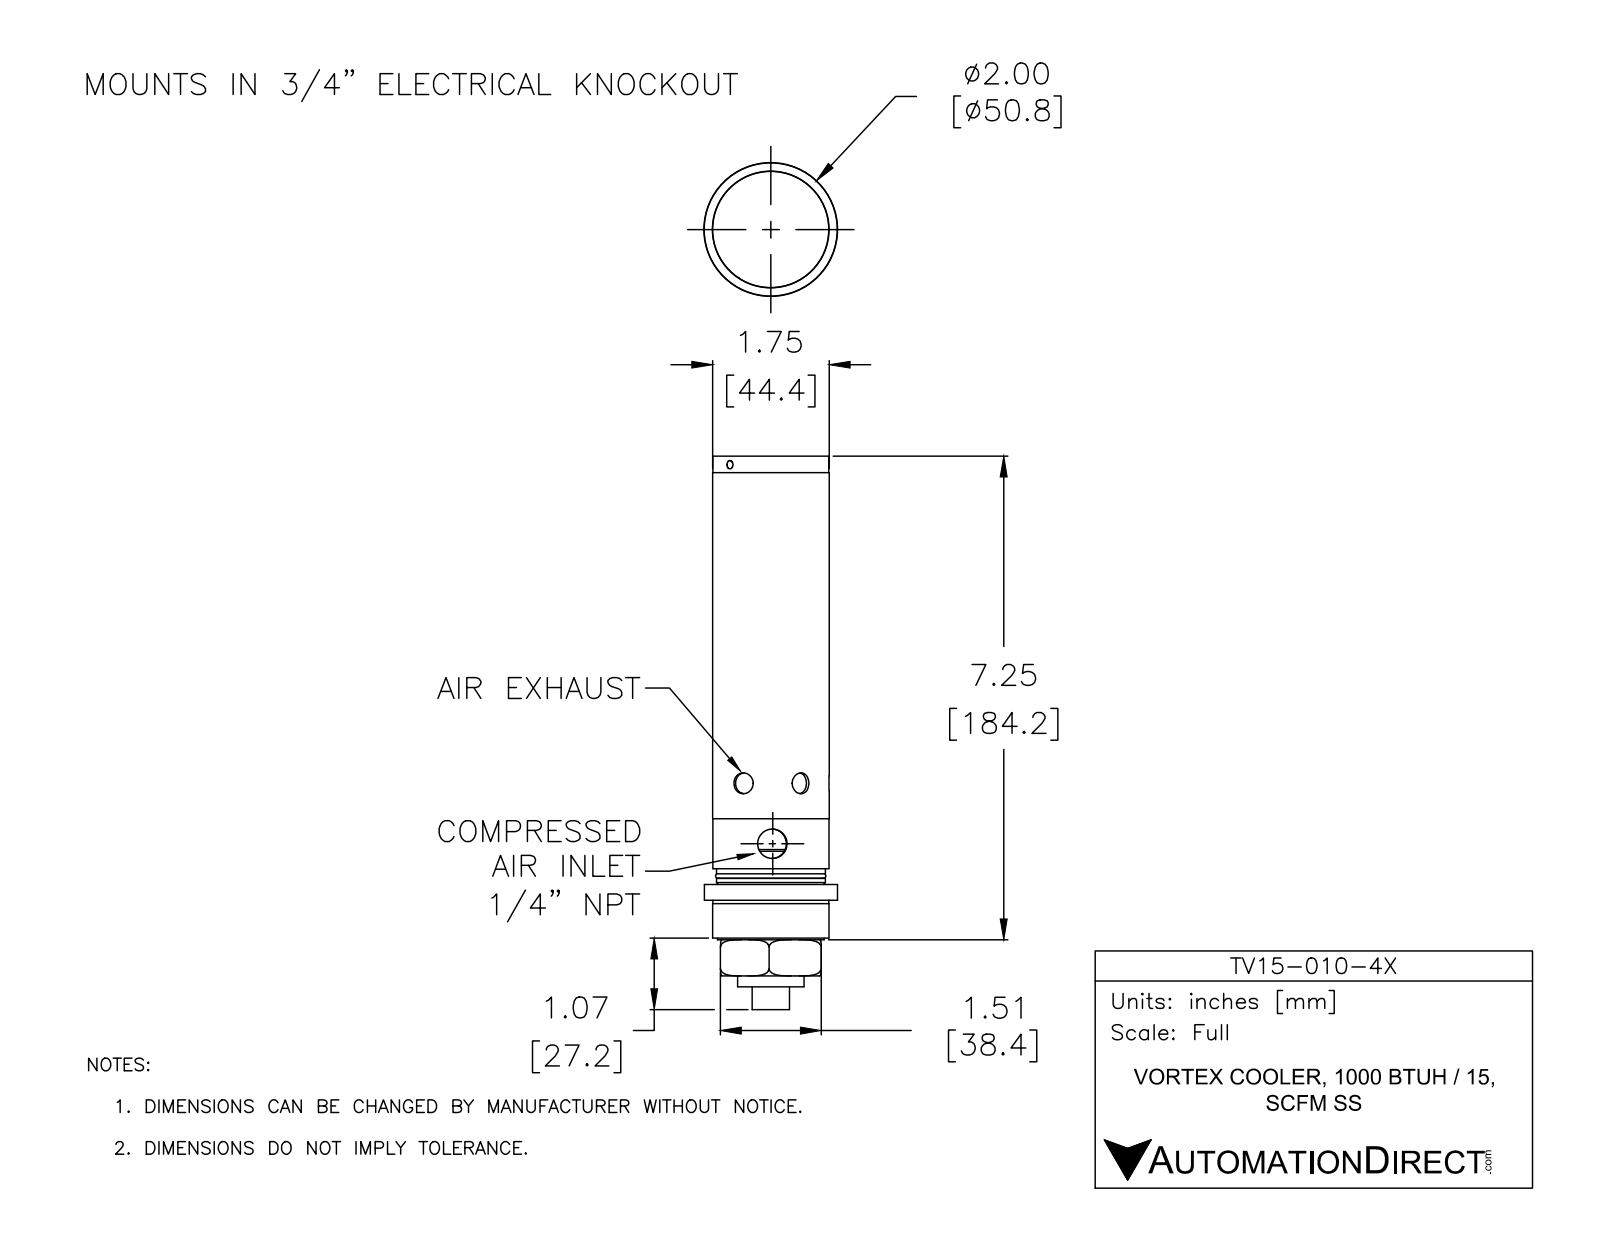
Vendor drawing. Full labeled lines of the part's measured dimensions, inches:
Part name (STEP PRODUCT): TV35-025-4X
STEP written by: SolidWorks 2017 (AUTOMOTIVE_DESIGN)
Units: inches
Bodies: 14 solids, 239 faces (90 planar, 86 cylindrical, 63 other)
Overall size (bounding box): 8.288 × 1.994 × 1.994
Volume: 13.07 in³ · Surface area: 173.3 in²
Round holes (diameter × count): ⌀0.313 ×3, ⌀0.25 ×2, ⌀0.251 ×2, ⌀0.125 ×1, ⌀0.327 ×1, ⌀0.36 ×1, ⌀0.387 ×1, ⌀0.44 ×1, ⌀0.47 ×1, ⌀0.512 ×1, ⌀0.575 ×1, ⌀0.785 ×1
Round bosses / shafts (diameter × count): ⌀1.994 ×1, ⌀1.747 ×1, ⌀1.746 ×1, ⌀1.741 ×1, ⌀1.738 ×1, ⌀1.736 ×1, ⌀1.7 ×1, ⌀1.633 ×1
Partial cylindrical surfaces — rounded edges, fillets, slot ends (radius × count): R0.005 ×6, R0.262 ×1
Main face-to-face distances: 1.221, 6.413, 5.192, 4.221, 3, 2.192, 0.83, 2.05, 5.05, 7.242
Hole centre spacings: 6.274
